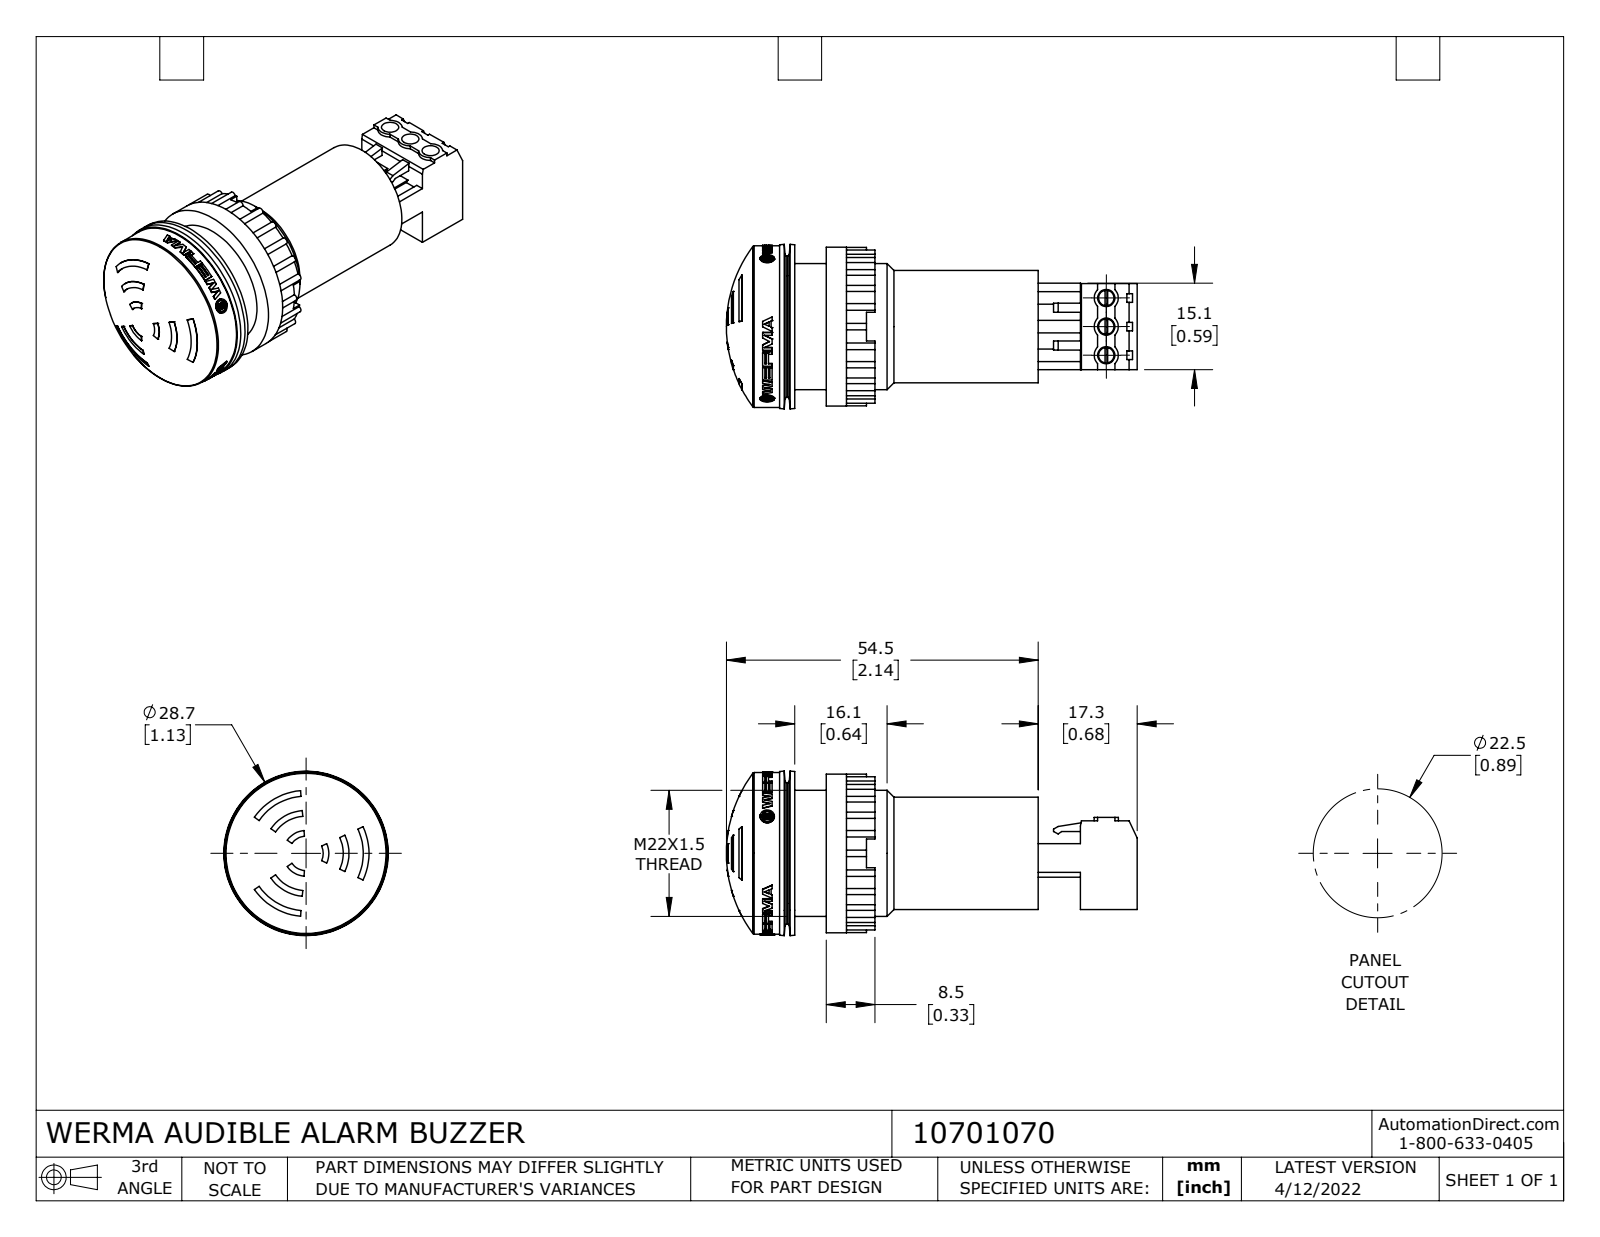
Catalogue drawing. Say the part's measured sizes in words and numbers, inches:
The part is named "10701070". Its 3-D file was written by "SolidWorks 2021 (CONFIG_CONTROL_DESIGN)". It is 1 solid with 617 faces: 321 planar, 148 cylindrical and 148 other. Overall it measures 2.82 by 1.13 by 1.13 inches. Its volume is 1.485 cubic inches and its surface area 11.49 square inches. Round holes: 3 of diameter 0.118. Round bosses or shafts: 3 of diameter 0.106, 1 of diameter 1.11, 1 of diameter 1.091, 1 of diameter 0.972, 1 of diameter 0.866, 1 of diameter 0.772. Partial cylindrical surfaces (rounded edges, fillets, slot ends): 24 of radius 0.023, 3 of radius 0.083, 3 of radius 0.112, 1 of radius 0.118, 1 of radius 0.157, 1 of radius 0.256, 1 of radius 0.295, 1 of radius 0.394. The main face-to-face distances are 1.457, 0.197, 0.591, 0.335, 0.291, 1.748, 1.413, 1.122, 0.39, 0.681. The hole center spacings are 0.197, 0.394.
